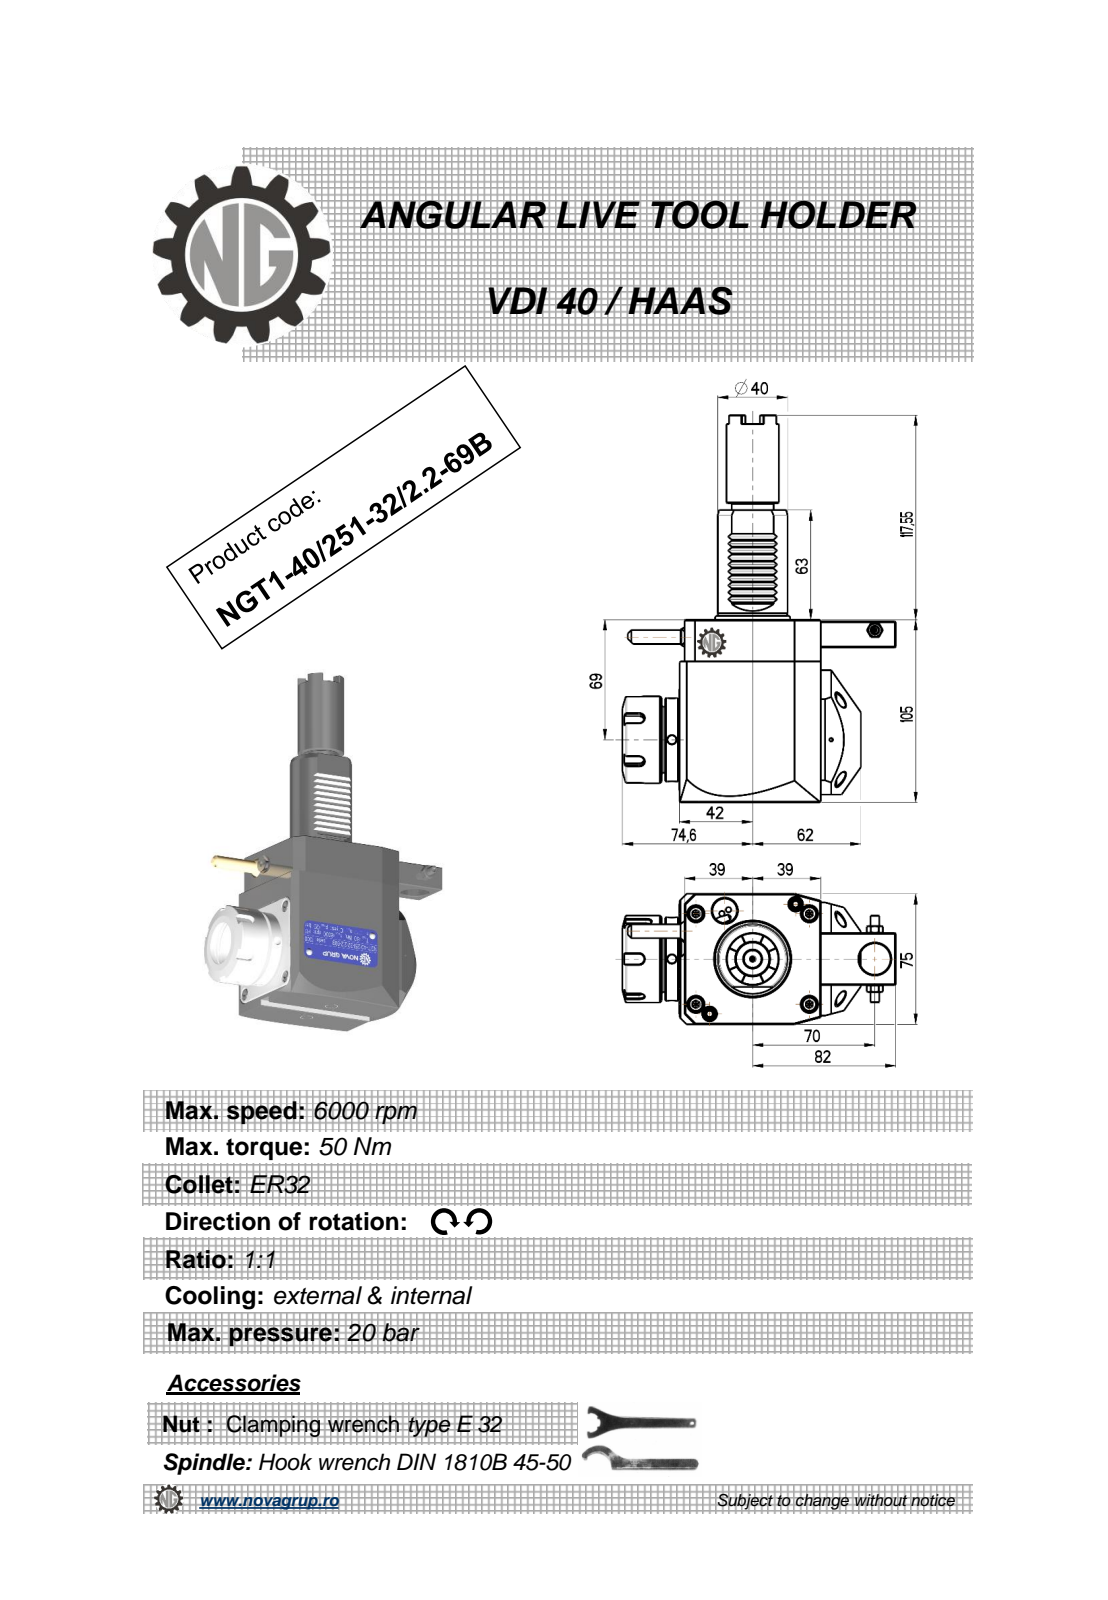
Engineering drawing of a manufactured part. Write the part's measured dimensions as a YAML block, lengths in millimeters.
part_name: "NGT1_40_251_32_2_2_69B"
step_written_by: "PRO/ENGINEER BY PARAMETRIC TECHNOLOGY CORPORATION, 2010280 (CONFIG_CONTROL_DESIGN)"
units: millimeters
bodies: {solids: 1, faces: 453, planar: 222, cylindrical: 94, other: 137}
overall_size: [222.55, 156.6, 76.6]
volume: 867965
surface_area: 74364
round_holes:
  - {diameter: 5, count: 3}
  - {diameter: 3, count: 1}
  - {diameter: 4.2, count: 1}
  - {diameter: 9.5, count: 1}
  - {diameter: 18, count: 1}
  - {diameter: 27, count: 1}
round_bosses_or_shafts:
  - {diameter: 50, count: 1}
  - {diameter: 48, count: 1}
  - {diameter: 41, count: 1}
  - {diameter: 40, count: 1}
  - {diameter: 30, count: 1}
  - {diameter: 24, count: 1}
  - {diameter: 10, count: 1}
  - {diameter: 8.96, count: 1}
partial_cylinders:
  - {radius: 0.26, count: 12}
  - {radius: 0.3, count: 10}
  - {radius: 0.2, count: 6}
  - {radius: 3, count: 5}
  - {radius: 0.5, count: 1}
  - {radius: 9.75, count: 1}
  - {radius: 40, count: 1}
face_to_face_distances: [75, 105, 81, 104, 80.8, 1, 101, 22.5, 3, 89]
hole_center_spacings: [16.19, 61.13, 61.5, 116.25, 132.22]
